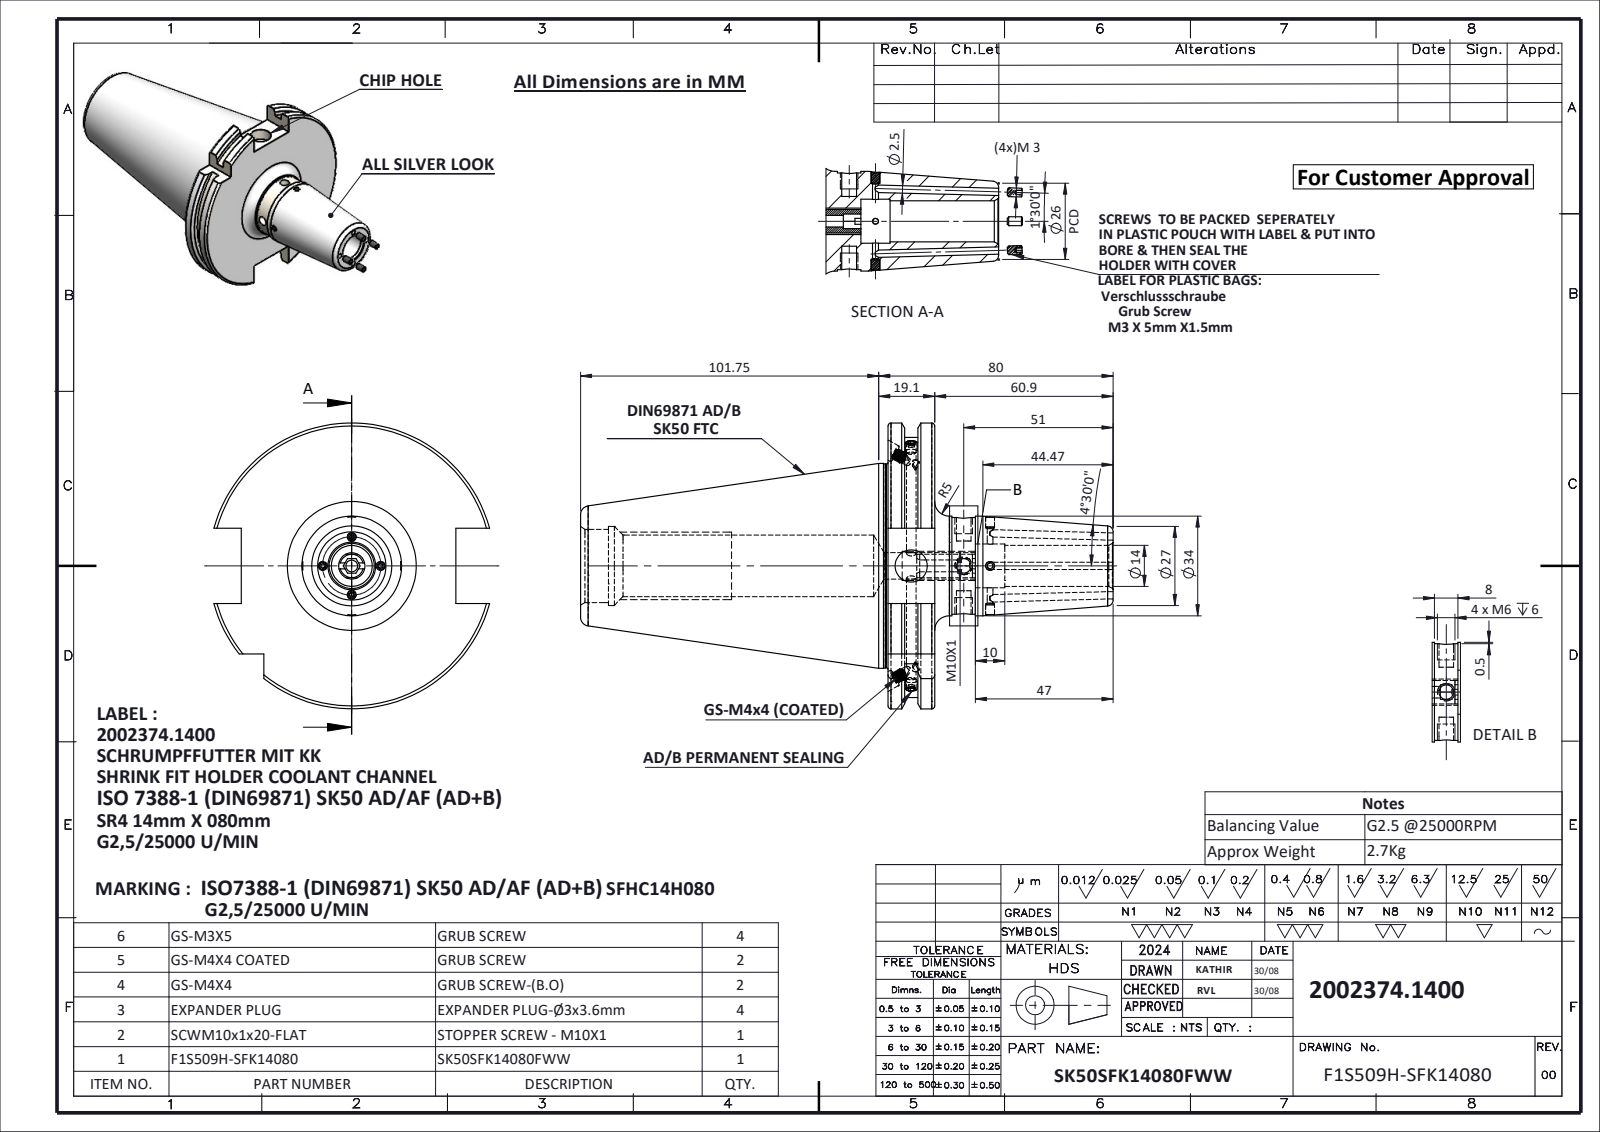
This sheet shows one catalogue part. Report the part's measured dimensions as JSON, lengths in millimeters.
{"part_name": "SK50SFK14080FWW; EXPANDER PLUG Ø3x3.6; F1S509H-SFK14080; GS-M3X5 (+3 more)", "step_written_by": "SolidWorks 2024 (CONFIG_CONTROL_DESIGN)", "units": "millimeters", "bodies": {"solids": 14, "faces": 452, "planar": 151, "cylindrical": 131, "other": 170}, "overall_size": [189.78, 97.5, 94.05], "volume_mm3": 362428, "surface_area_mm2": 56407, "round_holes": [[2.5, 4], [2, 2], [3, 2], [3.2, 2], [5, 2], [6, 2], [3.3, 1], [4, 1], [9, 1], [11, 1], [13.98, 1], [14.98, 1]], "round_bosses_or_shafts": [[4, 4], [3, 4], [2.9, 2], [69.85, 1], [69.45, 1], [34, 1], [33, 1]], "partial_cylinders_radius": [[5, 1], [44.9, 1], [48.75, 1]], "face_to_face_distances": [15.9, 5.66, 10.24, 10.14, 4.48, 5.76, 104.95, 110.61, 115.09, 120.85], "hole_center_spacings": [9, 17.9, 26.9]}
